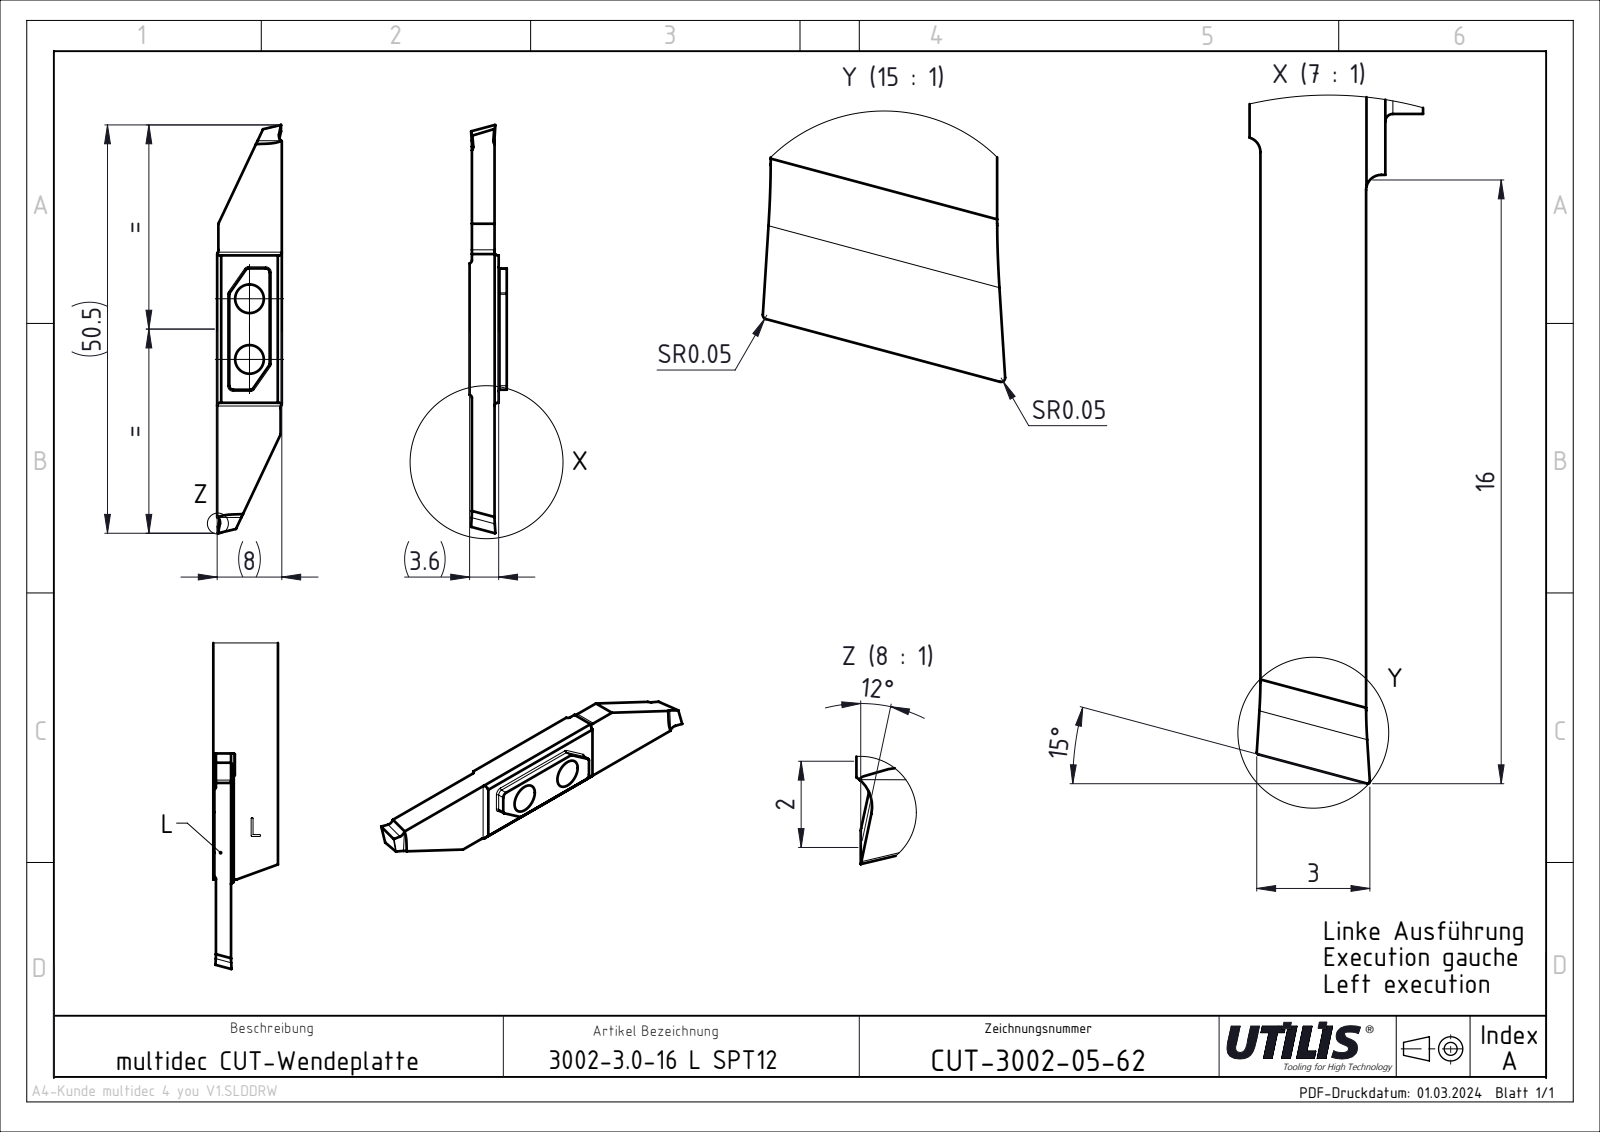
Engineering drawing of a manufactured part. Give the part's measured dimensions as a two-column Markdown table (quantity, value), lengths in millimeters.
| quantity | value |
| --- | --- |
| part name | CUT-3002 SPT Slim_and_Deep; ASME Y14.5 |
| STEP written by | SolidWorks 2023 SP4 \|\| FormatWorks Professional (AP242_MANAGED_MODEL_BASED_3D_ENGINEERING_MIM_LF) |
| units | millimeters |
| bodies | 1 solid, 36 faces (22 planar, 14 cylindrical, 0 other) |
| overall size | 50.5 × 8 × 3.6 |
| volume | 954 mm³ |
| surface area | 1 019 mm² |
| round holes (diameter × count) | 3.55 × 2 |
| partial cylindrical surfaces (radius × count) | 0.4 × 4, 1 × 2 |
| main face-to-face distances | 2.8, 3.09, 3.6, 3.31, 0.51, 8, 18.09, 7.85, 7.7, 0.42 |
| hole center spacings | 7.5 |
